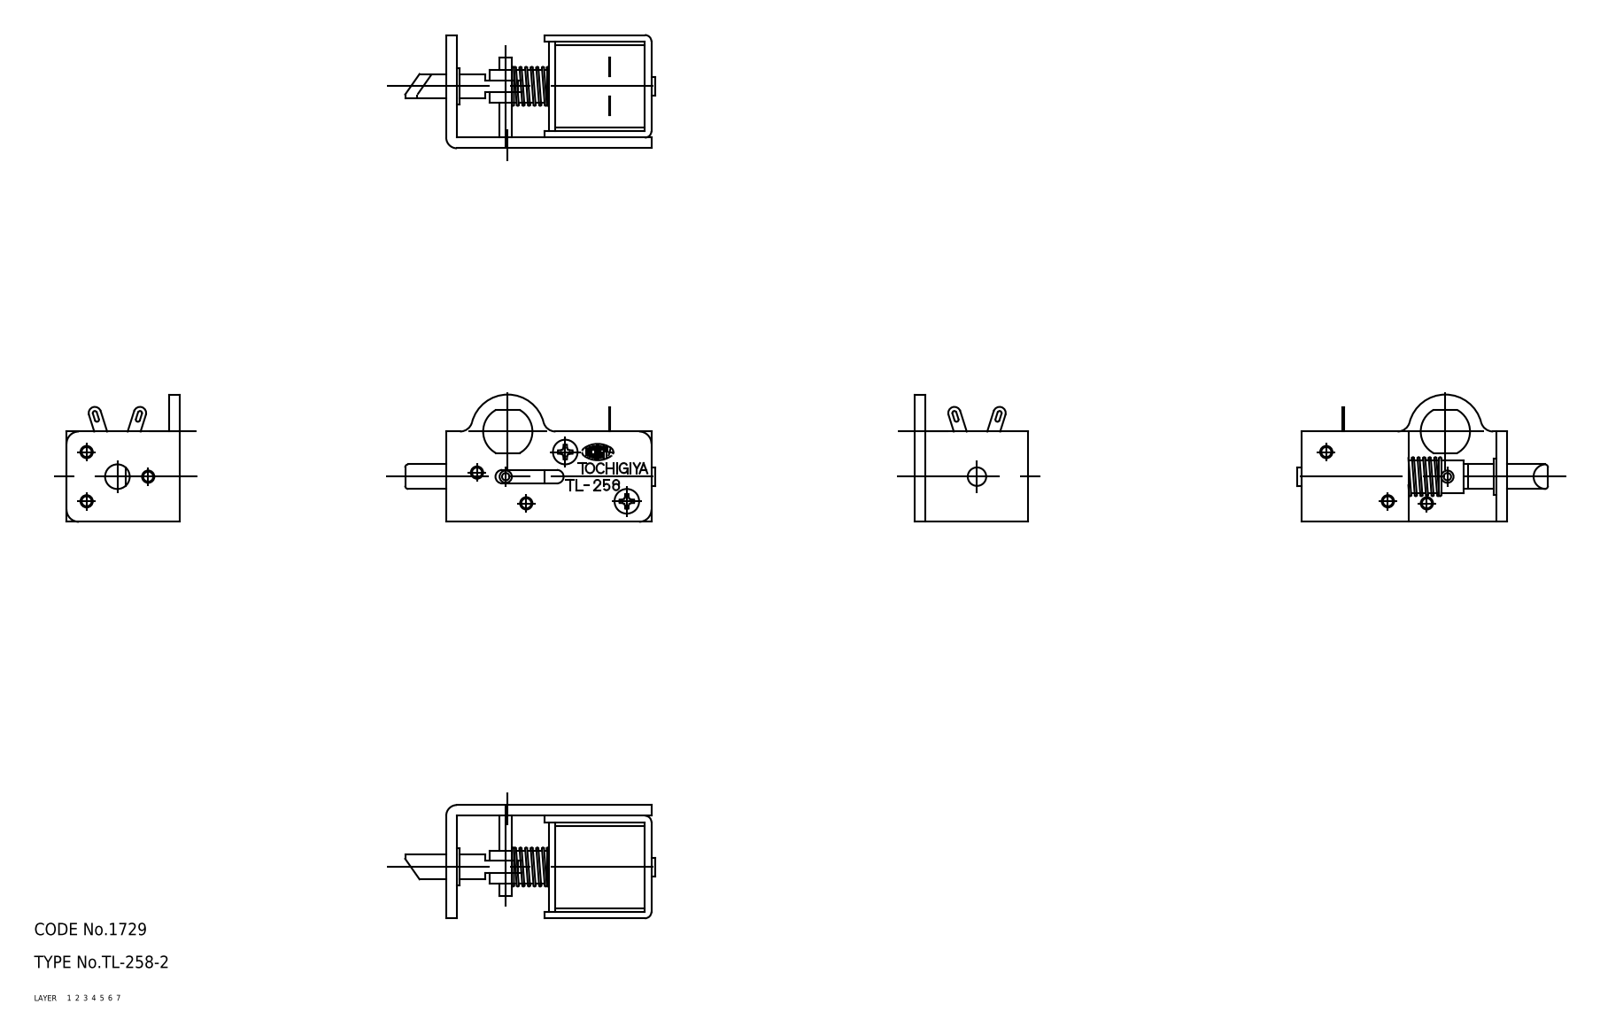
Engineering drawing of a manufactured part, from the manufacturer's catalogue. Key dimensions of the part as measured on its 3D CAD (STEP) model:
Part name (STEP PRODUCT): screw_1; spring; solenoid_2; solenoid_1 (+5 more)
STEP written by: CADfix (AUTOMOTIVE_DESIGN)
Units: millimetres
Bodies: 9 solids, 307 faces (0 planar, 0 cylindrical, 307 other)
Overall size (bounding box): 61 × 31 × 27.6
Volume: 15 381 mm³ · Surface area: 11 935 mm²
